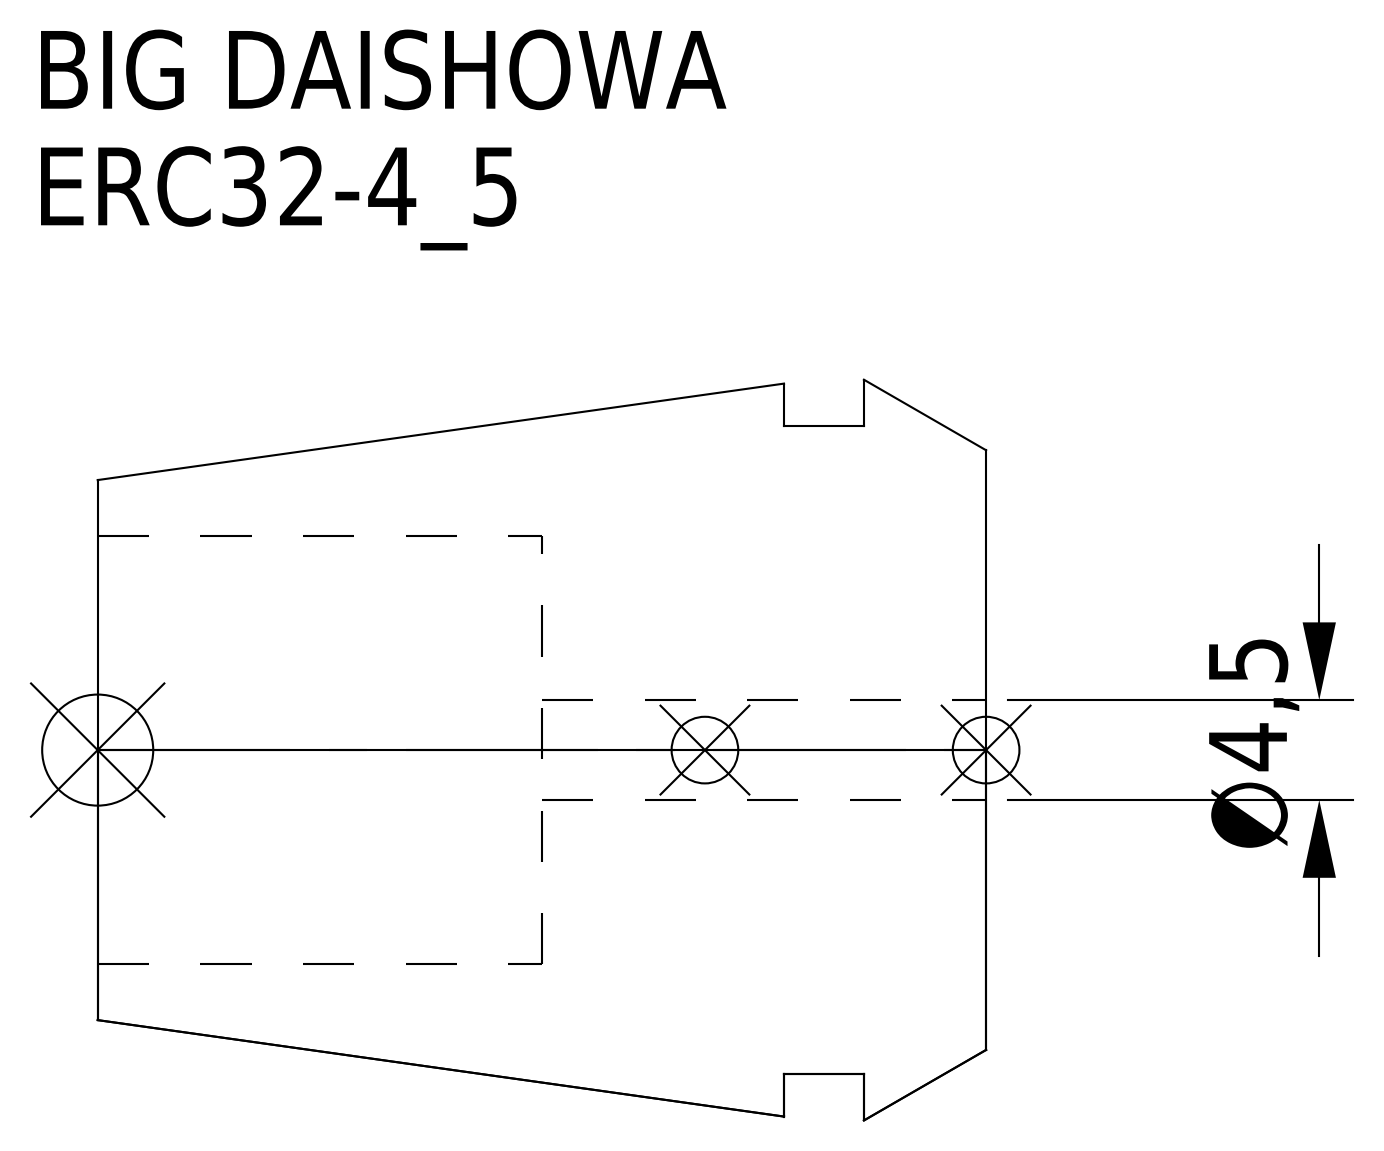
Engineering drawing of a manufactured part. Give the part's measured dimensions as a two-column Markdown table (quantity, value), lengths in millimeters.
| quantity | value |
| --- | --- |
| part name | ERC32-4_5 |
| STEP written by | CREO PARAMETRIC BY PTC INC, 2016380 (AUTOMOTIVE_DESIGN) |
| units | millimeters |
| bodies | 1 solid, 15 faces (5 planar, 6 cylindrical, 4 other) |
| overall size | 40 × 33.35 × 33.35 |
| volume | 20 273 mm³ |
| surface area | 6 632 mm² |
| round holes (diameter × count) | 4.5 × 1, 19.3 × 1 |
| round bosses / shafts (diameter × count) | 29.2 × 1 |
| main face-to-face distances | 20, 5.5, 14.5, 9.1, 3.6, 10.9, 40, 34.5, 30.9 |
